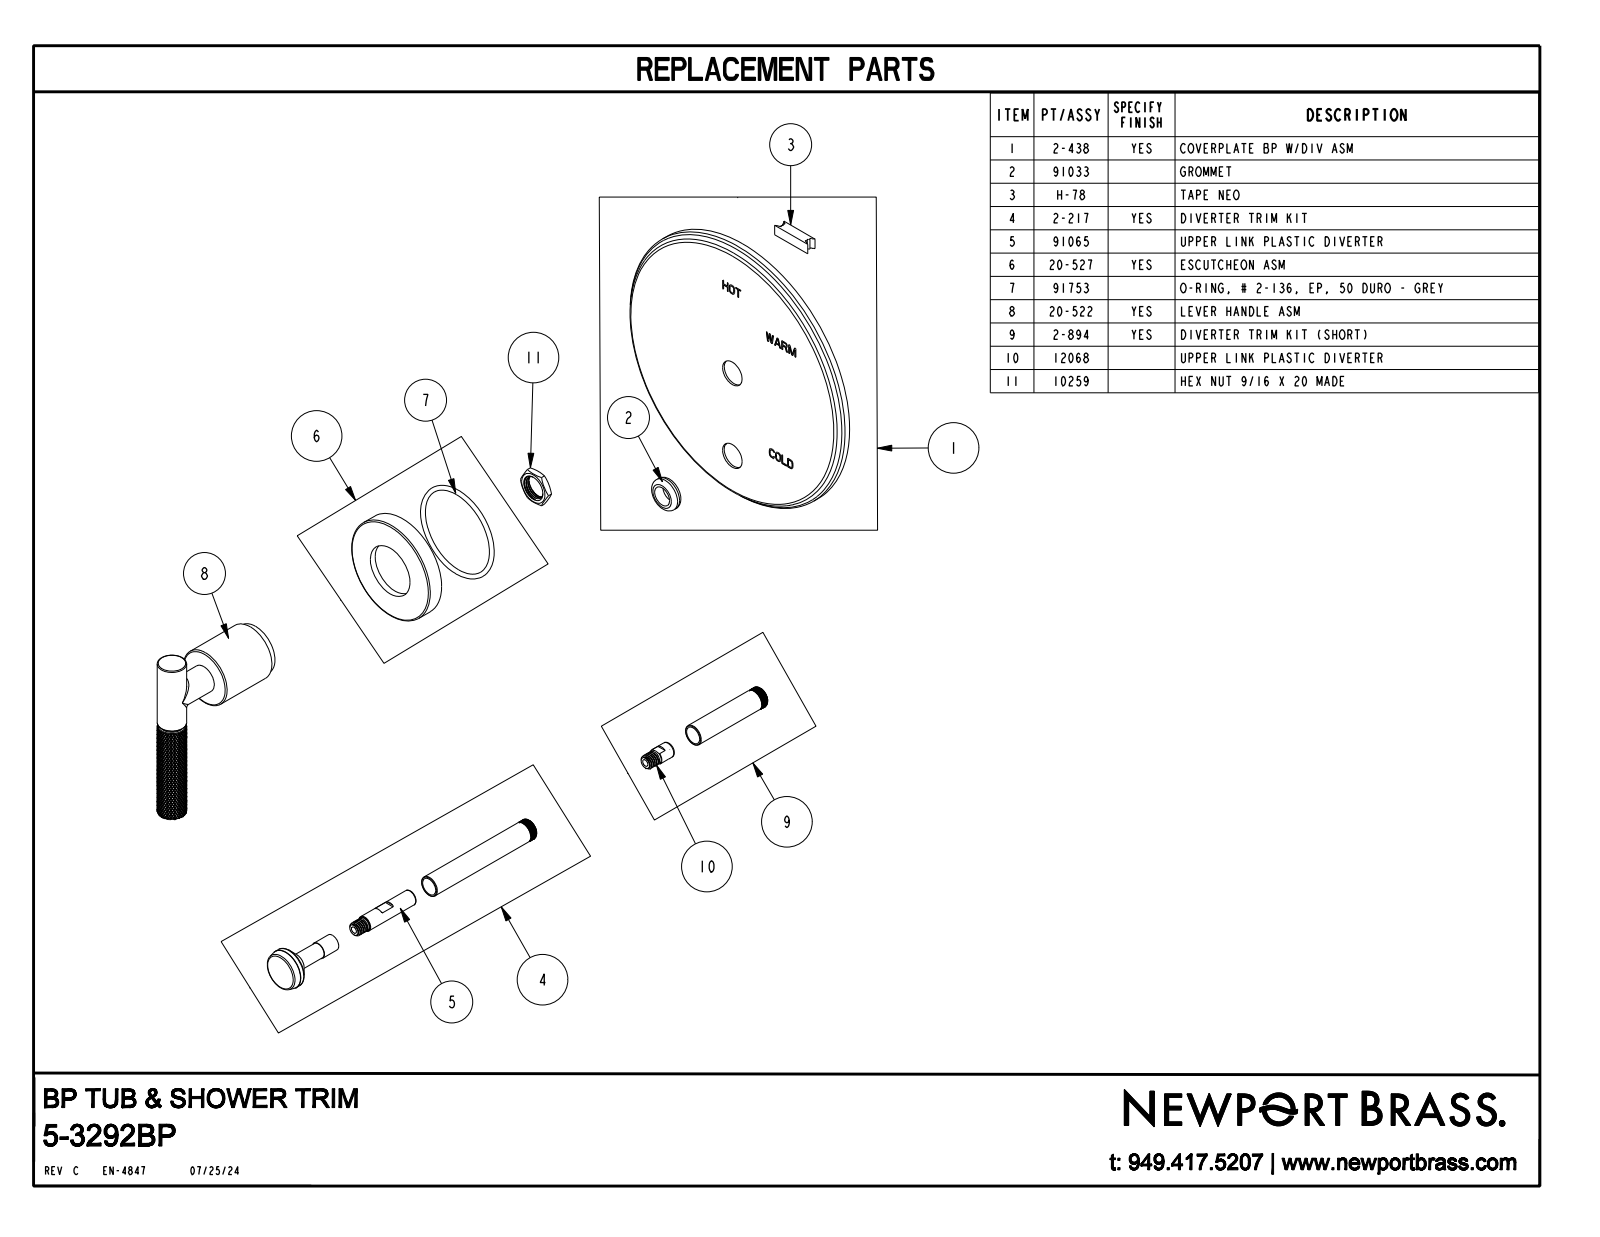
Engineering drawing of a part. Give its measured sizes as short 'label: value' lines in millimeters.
name: 5-3292BP
written by: CREO PARAMETRIC BY PTC INC, 2018400 (CONFIG_CONTROL_DESIGN)
unit: mm
bodies: 1 solid, 7895 faces (275 planar, 1512 cylindrical, 6108 other)
size: 165.1 × 165.1 × 86.2
volume: 253 500 mm³; area: 60 430 mm²
holes: 1× ⌀10, 1× ⌀13.6
bosses: 2× ⌀16, 1× ⌀165.1, 1× ⌀60.3, 1× ⌀33.4, 1× ⌀31.8, 1× ⌀22.9, 1× ⌀13, 1× ⌀12.7
face distances: 8, 17.5, 9.5, 53, 45.1, 35.6, 39.8, 31.8, 22.3, 13.3
hole spacings: 55.1
